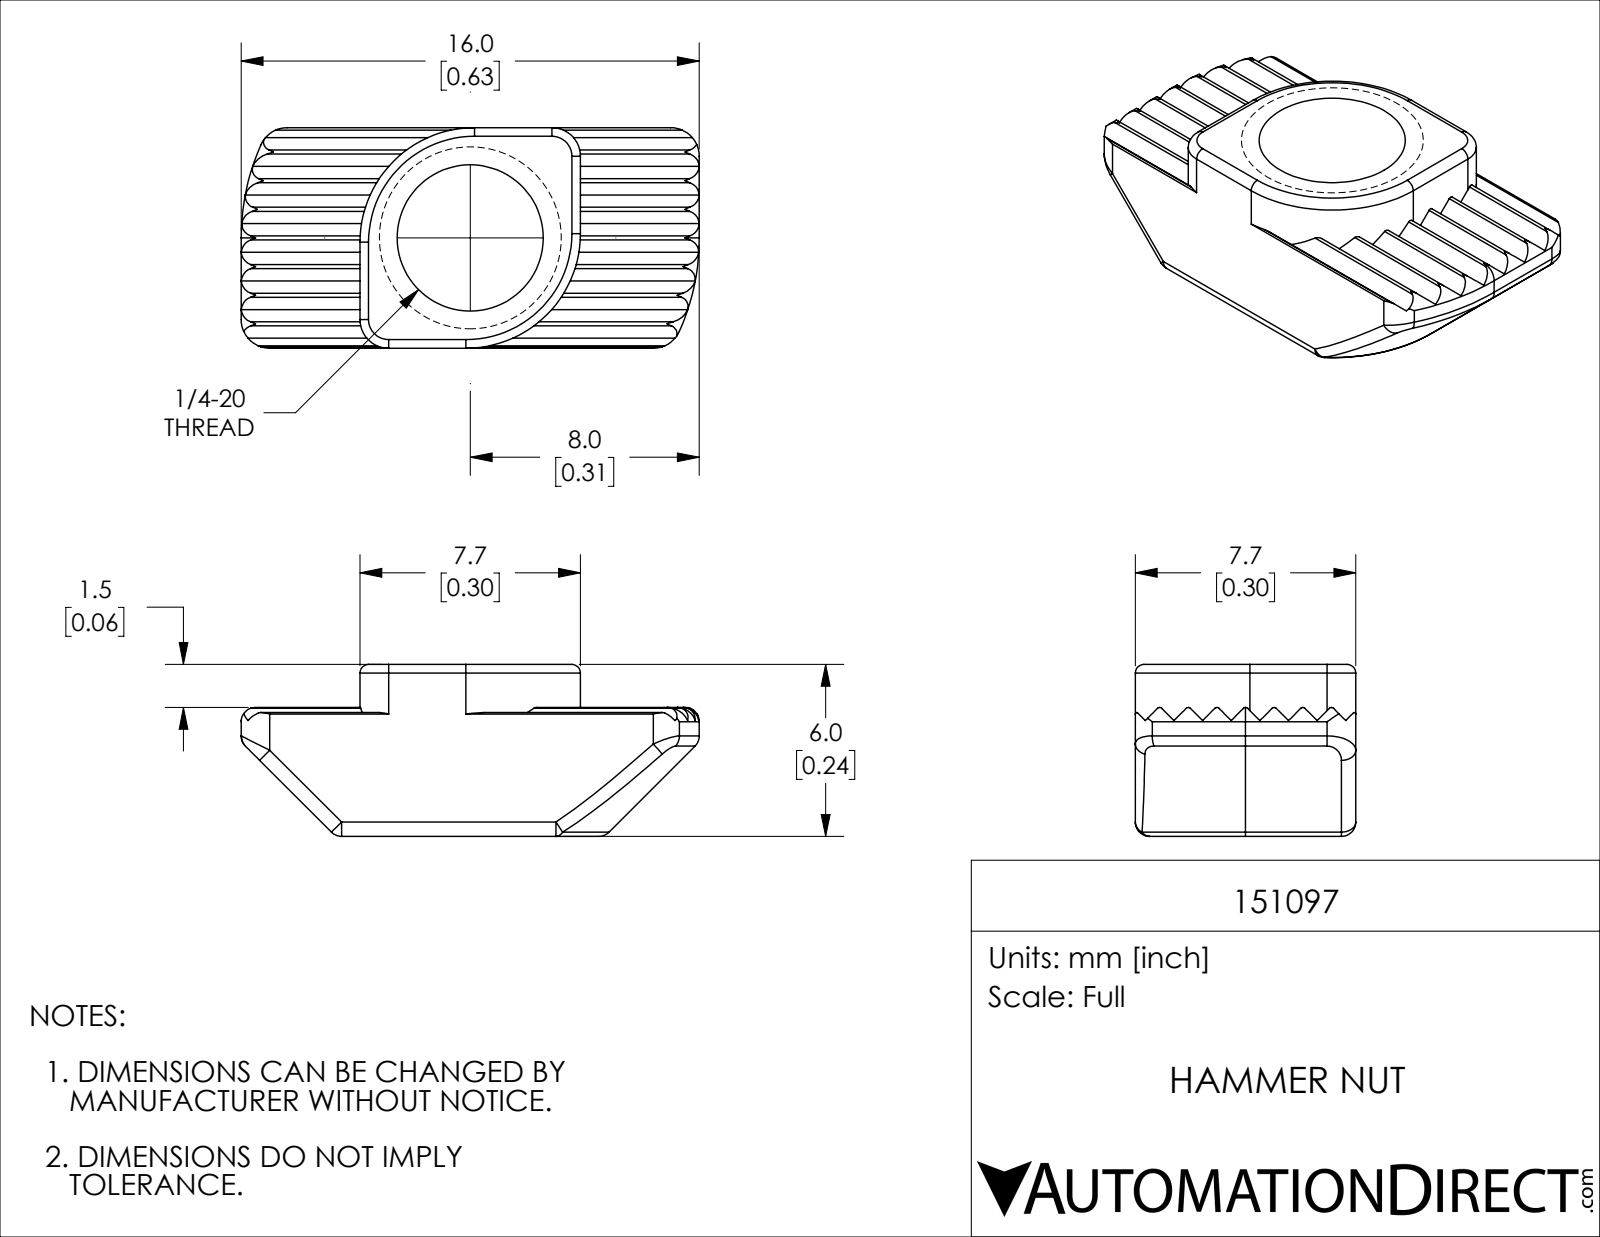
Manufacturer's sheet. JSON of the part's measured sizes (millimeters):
{"part_name": "151097", "step_written_by": "SolidWorks 2021 (CONFIG_CONTROL_DESIGN)", "units": "millimeters", "bodies": {"solids": 1, "faces": 110, "planar": 42, "cylindrical": 46, "other": 22}, "overall_size": [16, 7.7, 6], "volume_mm3": 394, "surface_area_mm2": 495, "round_holes": [[5.11, 1]], "partial_cylinders_radius": [[0.5, 10], [0.1, 7], [1, 6], [0.3, 4], [4, 2], [8, 1]], "face_to_face_distances": [7.7, 0.71, 2.12, 1.41, 2.83, 6, 3.53, 0.7, 4.24, 1.42]}
